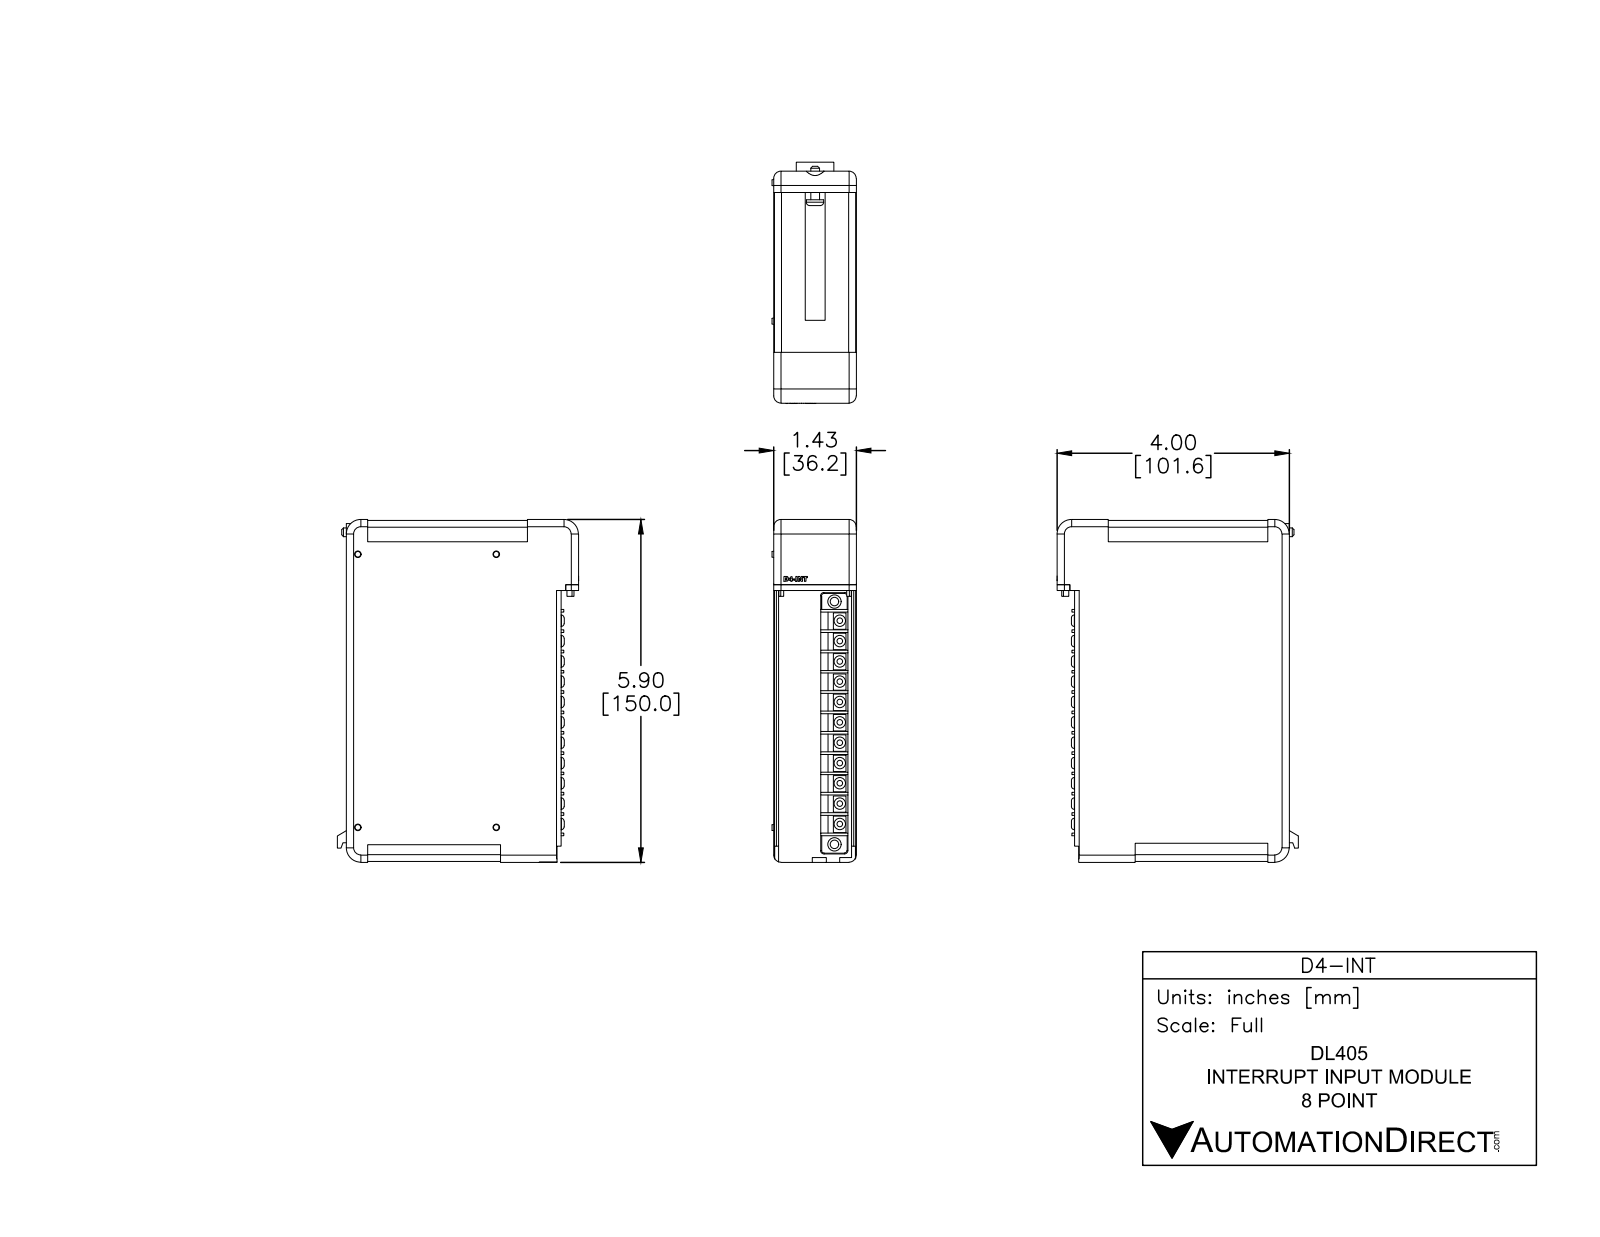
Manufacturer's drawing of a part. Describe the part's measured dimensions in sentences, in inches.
The part is named "D4-INT". Its 3-D file was written by "SolidWorks 2014 (AUTOMOTIVE_DESIGN)". It is 12 solids with 564 faces: 404 planar, 86 cylindrical and 74 other. Overall it measures 5.905 by 4.156 by 1.455 inches. Its volume is 27.51 cubic inches and its surface area 86.81 square inches. Round bosses or shafts: 21 of diameter 0.23, 2 of diameter 0.25, 1 of diameter 0.3, 1 of diameter 0.15. Partial cylindrical surfaces (rounded edges, fillets, slot ends): 8 of radius 0.125, 4 of radius 0.12, 3 of radius 0.25, 2 of radius 0.015, 2 of radius 0.03, 2 of radius 0.06, 1 of radius 0.149, 1 of radius 0.151. The main face-to-face distances are 1.425, 0.015, 2.89, 5.875, 1.41, 0.47, 0.2, 0.955, 5.89, 1.21.
